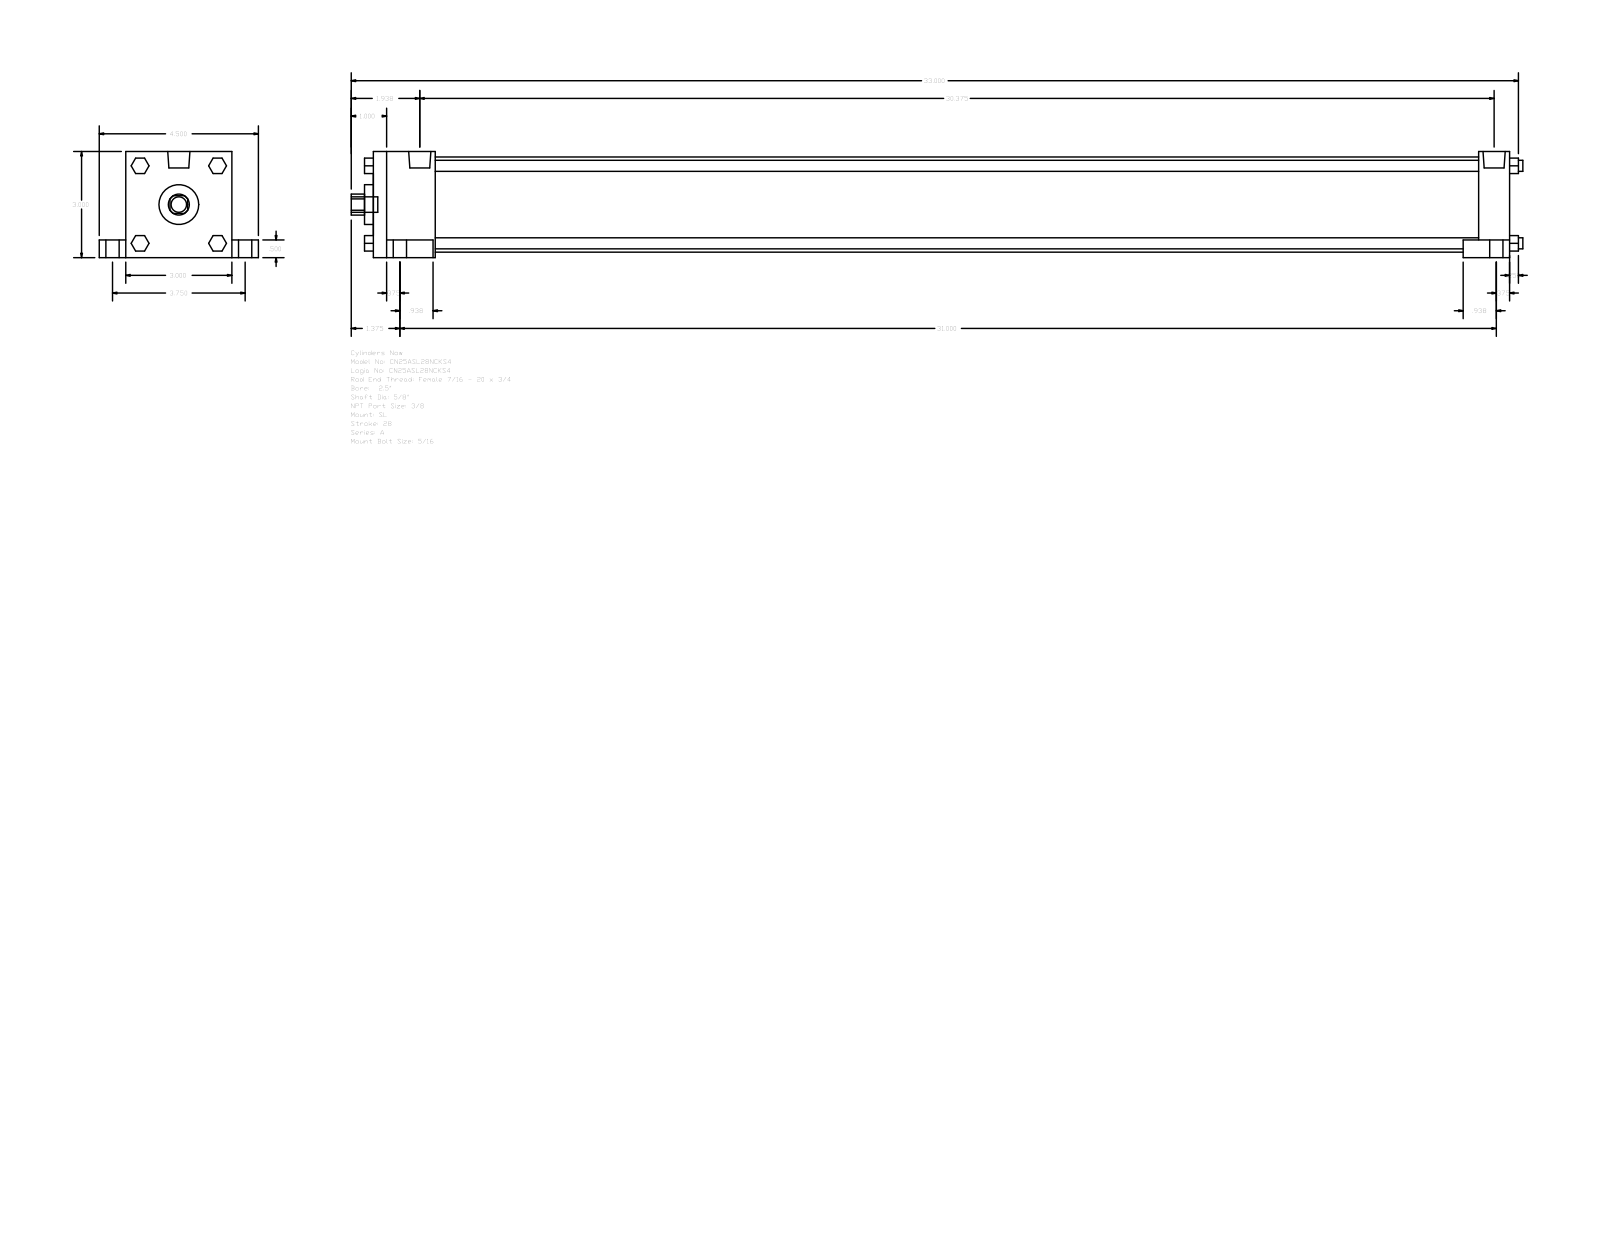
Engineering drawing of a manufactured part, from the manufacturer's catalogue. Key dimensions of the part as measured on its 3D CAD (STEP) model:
Part name (STEP PRODUCT): A_SL__0250_0.625
STEP written by: GSSL Pune (CONFIG_CONTROL_DESIGN)
Units: millimetres
Bodies: 0 solids, 148 faces (112 planar, 36 cylindrical, 0 other)
Overall size (bounding box): 841.38 × 114.3 × 76.2
Round holes (diameter × count): ⌀15.88 ×1, ⌀28.57 ×1, ⌀68.33 ×1
Round bosses / shafts (diameter × count): ⌀15.88 ×4, ⌀9.53 ×4, ⌀7.94 ×4, ⌀5.56 ×4, ⌀15.93 ×2, ⌀11.11 ×1
Partial cylindrical surfaces — rounded edges, fillets, slot ends (radius × count): R7.54 ×1
Main face-to-face distances: 76.2, 815.97, 44.45, 771.52, 793.74, 749.29, 22.23, 12.7, 63.5, 19.05
